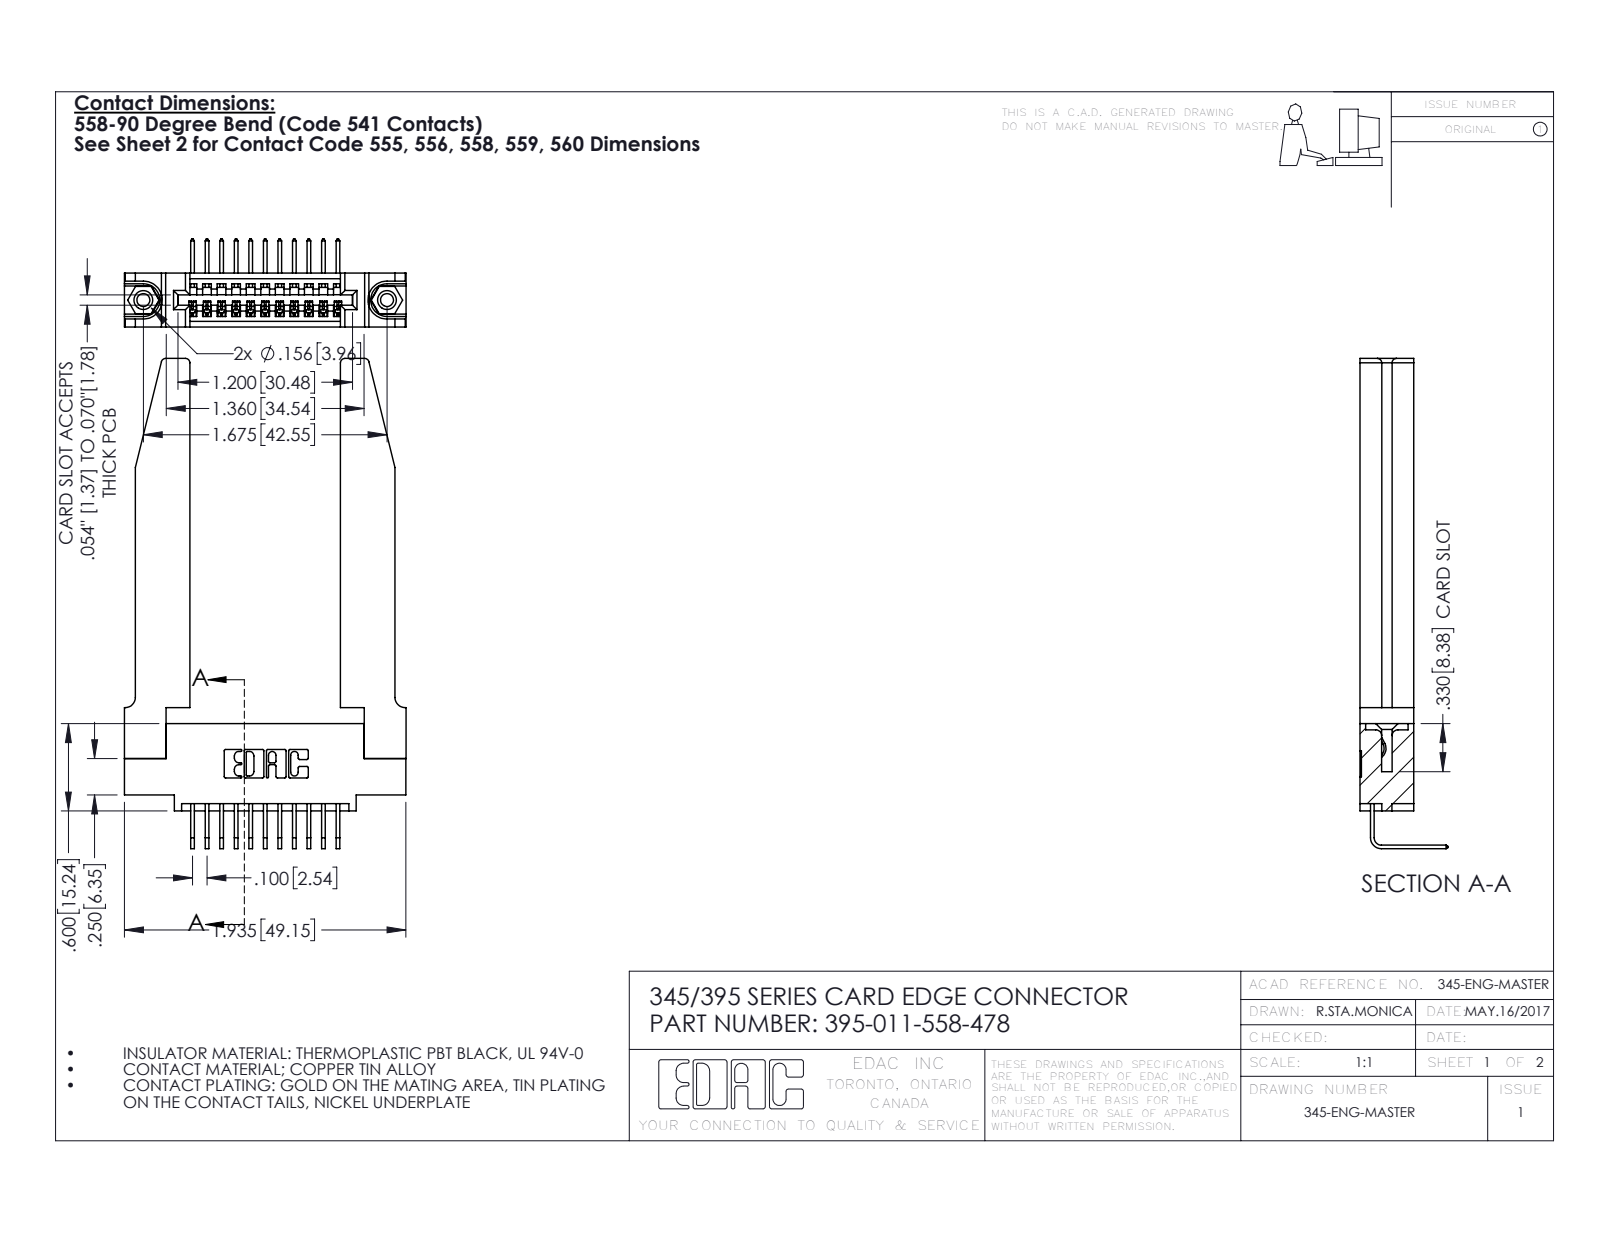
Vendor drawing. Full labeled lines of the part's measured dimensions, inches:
Part name (STEP PRODUCT): 345-292-001_558 Tail - 2; 345 Part_0.110 Offset - 0.156 Dia-TH; 345-220-078_345-220-078; 345-250-001_345-250-001-102 (+1 more)
STEP written by: SolidWorks 2016 (CONFIG_CONTROL_DESIGN)
Units: inches
Bodies: 16 solids, 1024 faces (688 planar, 284 cylindrical, 52 other)
Overall size (bounding box): 3.369 × 1.936 × 0.605
Volume: 0.741 in³ · Surface area: 19.44 in²
Round holes (diameter × count): ⌀0.089 ×2, ⌀0.125 ×2, ⌀0.156 ×2, ⌀0.064 ×1
Round bosses / shafts (diameter × count): ⌀0.155 ×2
Partial cylindrical surfaces — rounded edges, fillets, slot ends (radius × count): R0.006 ×22, R0.01 ×22, R0.03 ×8, R0.007 ×6, R0.031 ×6, R0.026 ×3, R0.031 ×2, R0.04 ×2
Main face-to-face distances: 0.37, 0.072, 0.298, 0.148, 0.15, 0.22, 0.077, 1.035, 0.2, 0.098
Hole centre spacings: 0.27, 1.443, 1.675
